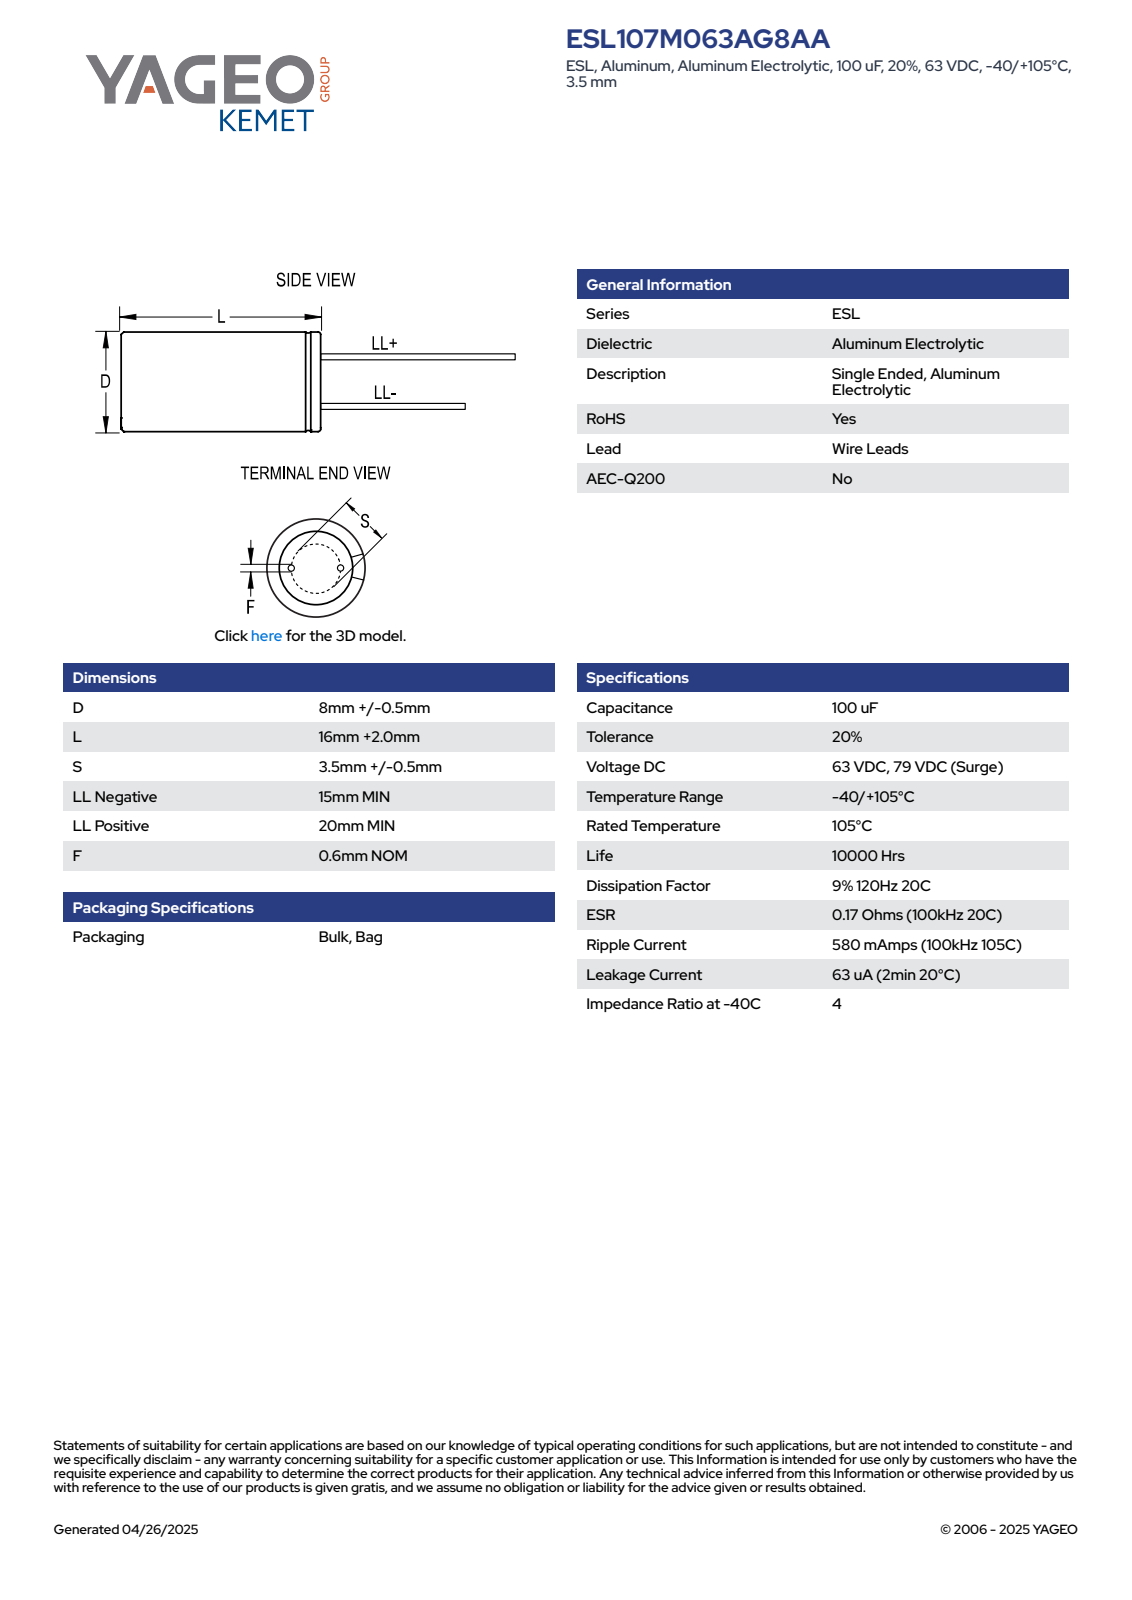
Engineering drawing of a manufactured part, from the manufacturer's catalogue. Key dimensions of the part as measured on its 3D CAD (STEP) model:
Part name (STEP PRODUCT): CAR_KLP_8X16_D8.5L18S3.5F0.6
STEP written by: SolidWorks 2014 (AUTOMOTIVE_DESIGN)
Units: millimetres
Bodies: 4 solids, 75 faces (61 planar, 8 cylindrical, 6 other)
Overall size (bounding box): 38.01 × 8.5 × 8.5
Volume: 1 025 mm³ · Surface area: 676 mm²
Round bosses / shafts (diameter × count): ⌀0.6 ×2, ⌀8.5 ×1
Main face-to-face distances: 18, 18.01, 33.01, 38.01, 33, 38, 15, 20, 5, 1.15
